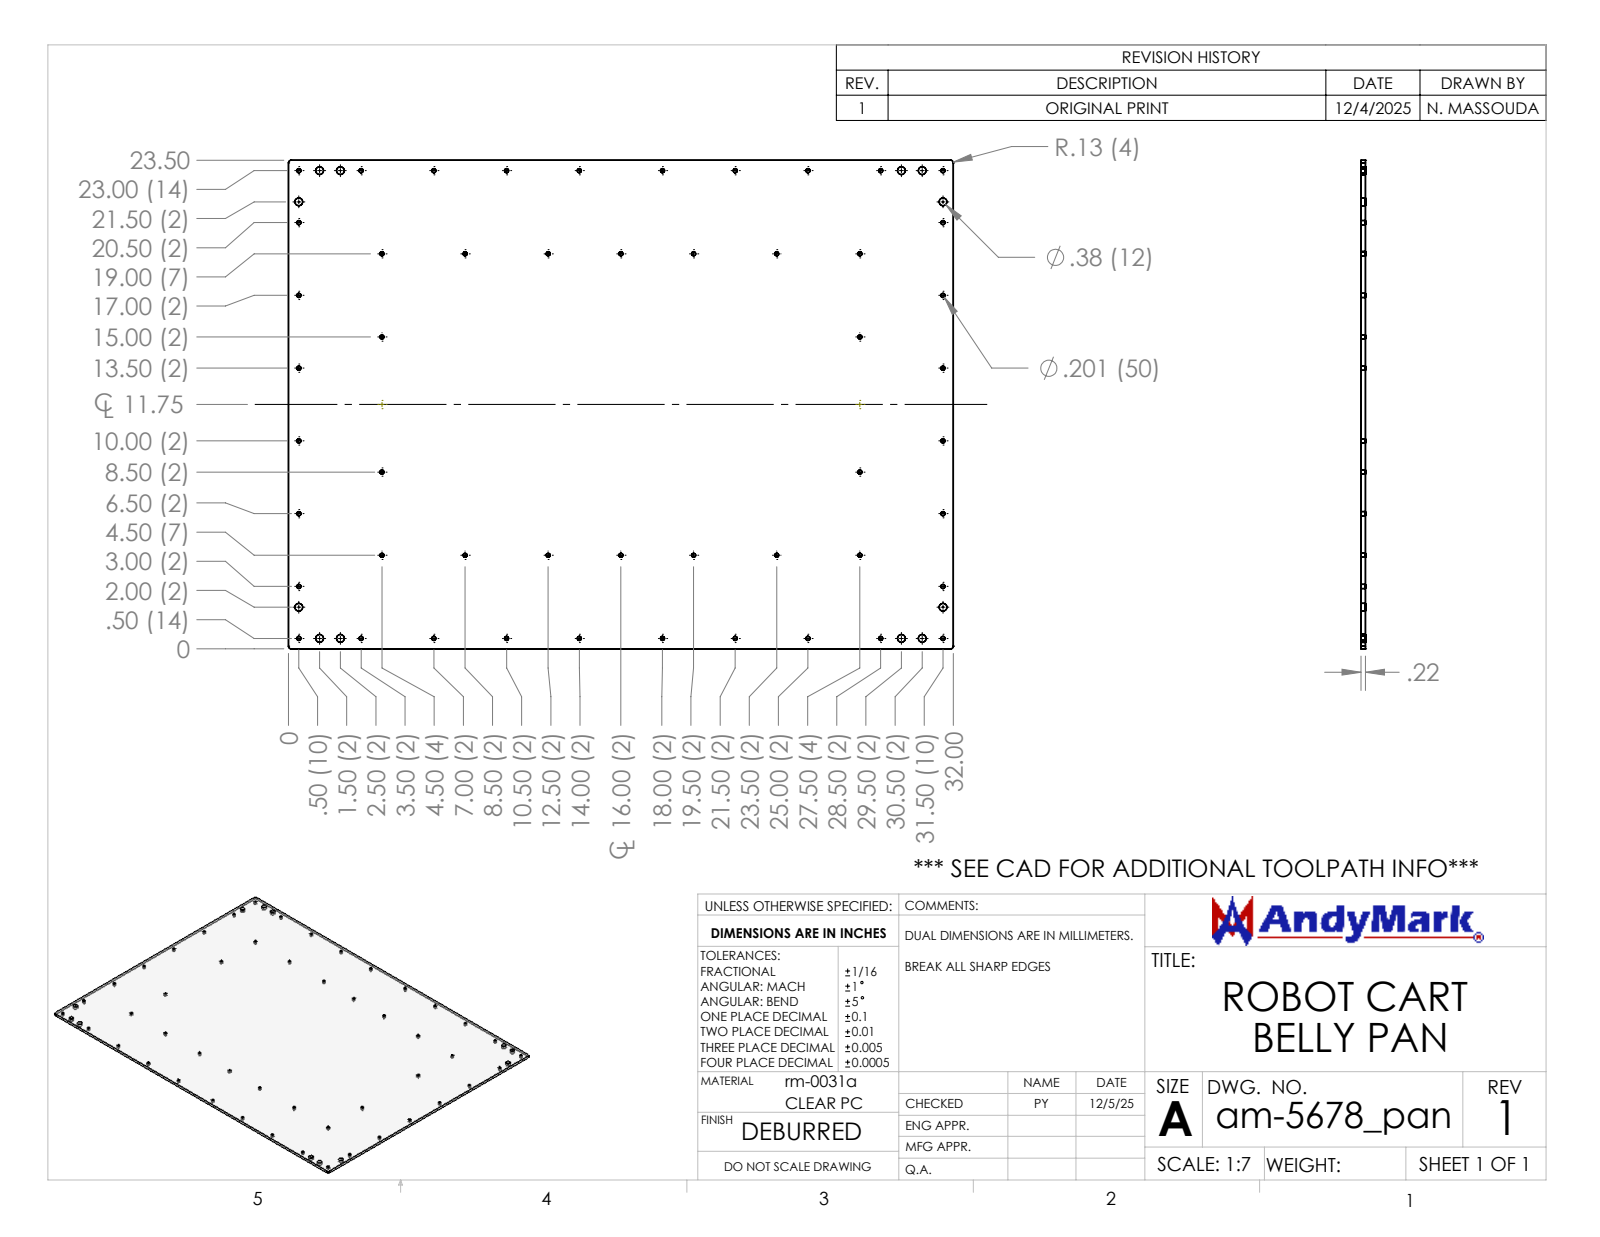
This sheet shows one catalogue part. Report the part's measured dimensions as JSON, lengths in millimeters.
{"part_name": "am-5678_pan Robot Cart Belly Pan", "step_written_by": "SolidWorks 2024 (AUTOMOTIVE_DESIGN)", "units": "millimeters", "bodies": {"solids": 1, "faces": 134, "planar": 6, "cylindrical": 128, "other": 0}, "overall_size": [812.8, 596.9, 5.6], "volume_mm3": 2701000, "surface_area_mm2": 989000, "round_holes": [[5.1, 50], [9.5, 12]], "partial_cylinders_radius": [[3.2, 4]], "face_to_face_distances": [5.6, 596.9, 812.8], "hole_center_spacings": [88.9, 25.4, 571.5, 114.3, 578.4, 177.8, 572.1, 787.4]}
